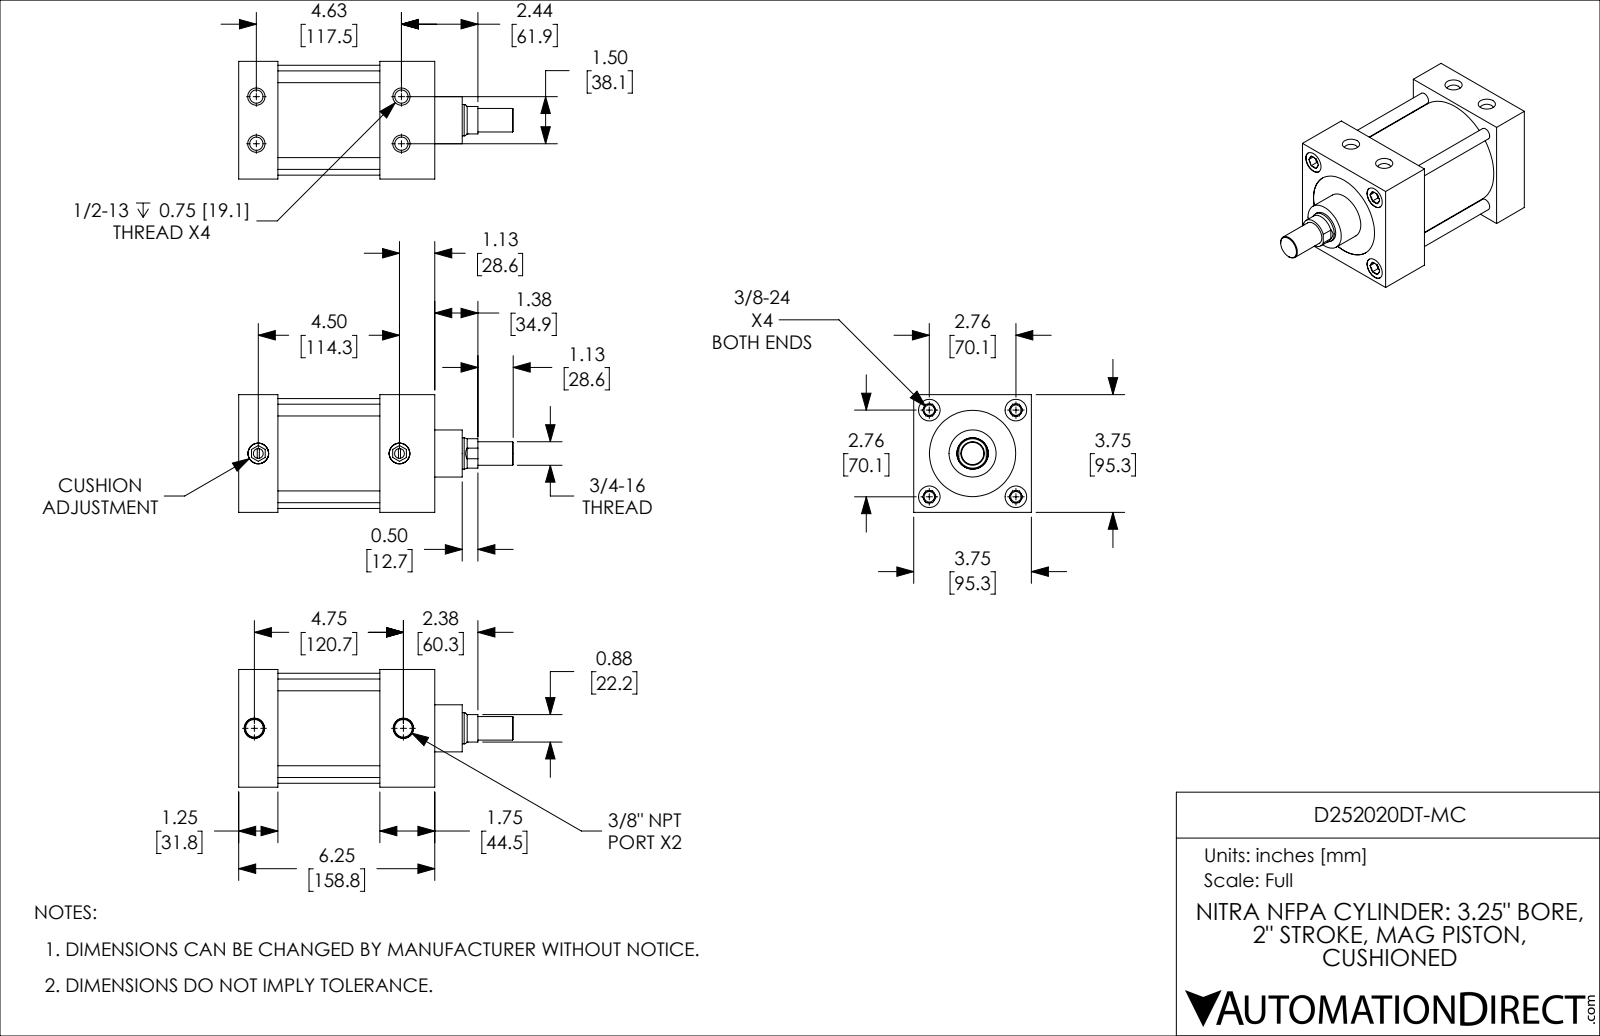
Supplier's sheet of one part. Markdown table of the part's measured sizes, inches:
| quantity | value |
| --- | --- |
| part name | D252020DT-MC_BODY; D252020DT-MC_PISTON_KK1; D252020DT-MC; D252020DT-MC_CUSHION |
| STEP written by | SolidWorks 2019 (CONFIG_CONTROL_DESIGN) |
| units | inches |
| bodies | 4 solids, 246 faces (90 planar, 78 cylindrical, 78 other) |
| overall size | 8.75 × 3.75 × 3.75 |
| volume | 59.91 in³ |
| surface area | 263.9 in² |
| round holes (diameter × count) | 0.332 × 4, 0.422 × 4, 0.687 × 4, 0.312 × 2, 0.562 × 2, 0.656 × 2, 1.001 × 1, 2.75 × 1, 3.251 × 1 |
| round bosses / shafts (diameter × count) | 0.375 × 4, 0.657 × 2, 3.501 × 1, 3.249 × 1, 1.5 × 1, 0.999 × 1, 0.75 × 1 |
| partial cylindrical surfaces (radius × count) | 0.469 × 1 |
| main face-to-face distances | 1.25, 3.75, 4.5, 3.25, 3.75, 2.5, 2, 6.25, 5, 1.75 |
| hole center spacings | 0.753, 1.952, 2.76, 4.747, 1.5, 3.903, 4.625, 4.862 |
